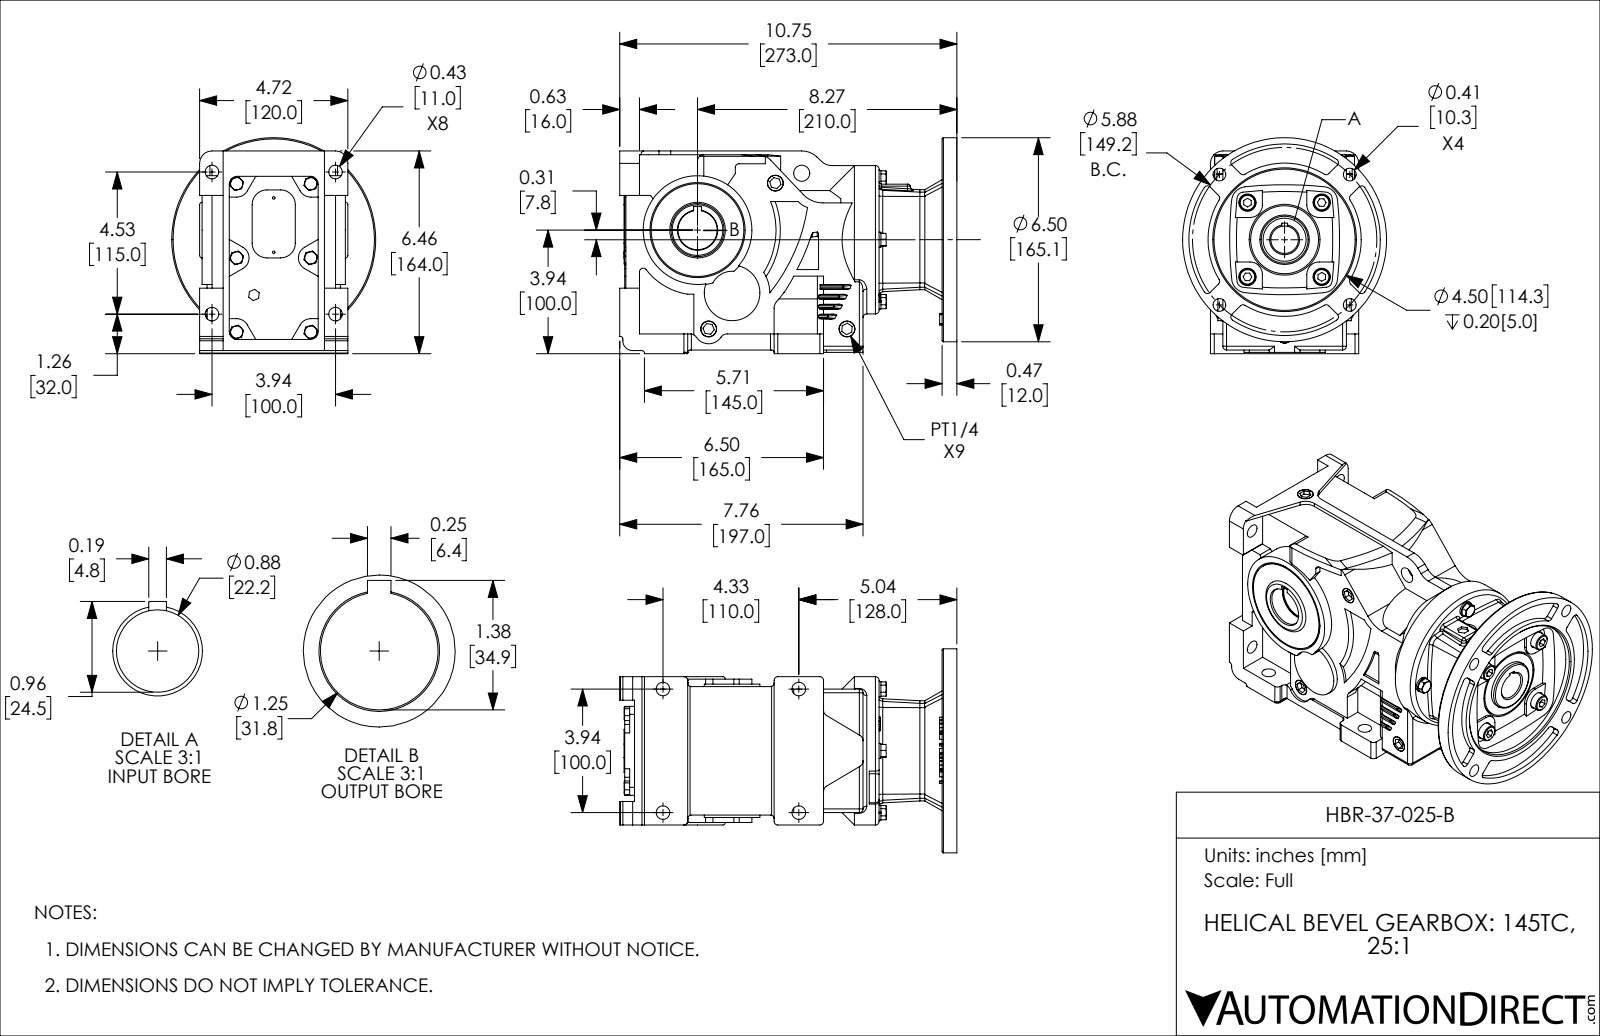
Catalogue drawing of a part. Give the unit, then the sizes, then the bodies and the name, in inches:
Units: inches
Overall size (bounding box): 10.748 × 6.88 × 6.5
Round holes (diameter × count): ⌀0.433 ×8, ⌀0.24 ×4, ⌀0.276 ×4, ⌀0.406 ×4, ⌀0.551 ×4, ⌀0.079 ×2, ⌀0.512 ×1, ⌀0.875 ×1, ⌀1.25 ×1, ⌀1.327 ×1, ⌀4.5 ×1
Round bosses / shafts (diameter × count): ⌀0.512 ×4, ⌀0.48 ×4, ⌀0.236 ×4, ⌀6.5 ×1, ⌀4.724 ×1, ⌀3.465 ×1, ⌀2.953 ×1, ⌀2.165 ×1
Partial cylindrical surfaces — rounded edges, fillets, slot ends (radius × count): R0.118 ×38, R0.039 ×18, R0.394 ×14, R0.197 ×11, R0.079 ×10, R0.472 ×6, R0.157 ×4, R0.256 ×4
Main face-to-face distances: 0.472, 0.315, 0.118, 0.157, 0.079, 4.252, 0.276, 0.394, 3.937, 0.512
Hole centre spacings: 2.08, 4.548, 3.937, 1.42, 1.673, 1.969, 2.784, 2.937
Volume: 210.9 in³ · Surface area: 395.6 in²
Bodies: 1 solid, 1103 faces (542 planar, 292 cylindrical, 269 other)
Part name (STEP PRODUCT): HBR-37-025-B
STEP written by: SolidWorks 2018 (AUTOMOTIVE_DESIGN)
